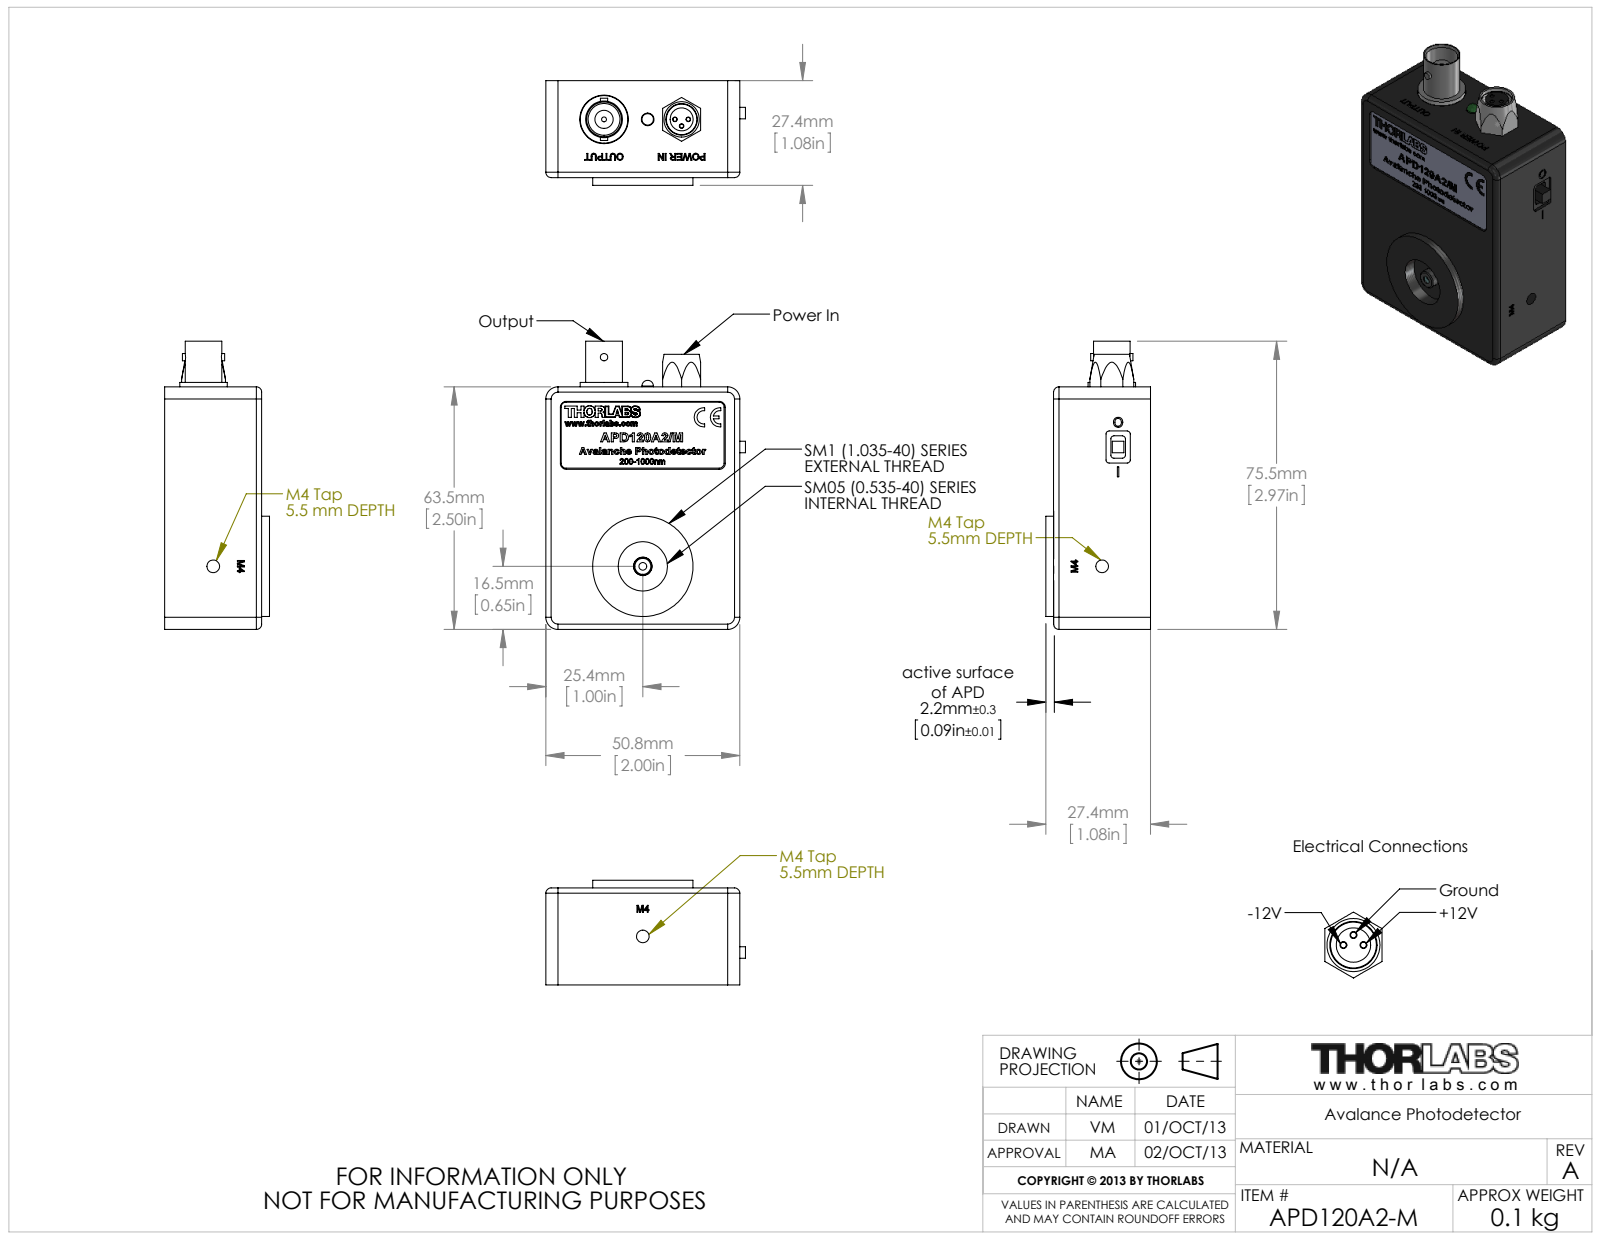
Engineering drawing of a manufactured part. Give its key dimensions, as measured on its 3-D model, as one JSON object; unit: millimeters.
{"part_name": "APD120A2M-Baugruppe; APD120x-Folie_APD120A2-M; countersunk flat head cross recess screw_din_ISO 7046-1 - M2 x 4 - Z --- 4N; M0092-0545-0A-Deckel (+7 more)", "step_written_by": "SolidWorks 2012 (CONFIG_CONTROL_DESIGN)", "units": "millimeters", "bodies": {"solids": 77, "faces": 2285, "planar": 1451, "cylindrical": 283, "other": 551}, "overall_size": [75.46, 52.26, 27.43], "volume_mm3": 39549, "surface_area_mm2": 33784, "round_holes": [[1.6, 8], [2.4, 4], [2.44, 4], [0.46, 3], [1, 3], [1.02, 3], [3.3, 2], [1.27, 1], [1.32, 1], [2, 1], [2.5, 1], [3.3, 1]], "round_bosses_or_shafts": [[0.51, 6], [3.8, 5], [2, 4], [0.45, 3], [26.29, 1], [12.45, 1], [10.92, 1], [9.6, 1]], "partial_cylinders_radius": [[3.17, 18], [3.3, 14], [0.8, 10], [0.79, 8], [1.91, 8], [2.41, 8], [1.27, 4], [1.4, 4]], "face_to_face_distances": [1.59, 11.49, 13.08, 2.54, 9.89, 1.6, 11.48, 25.4, 23.81, 13.92], "hole_center_spacings": [41.17, 39.38, 4.41, 20.89, 21.35, 51.14, 65.51, 1.27]}
